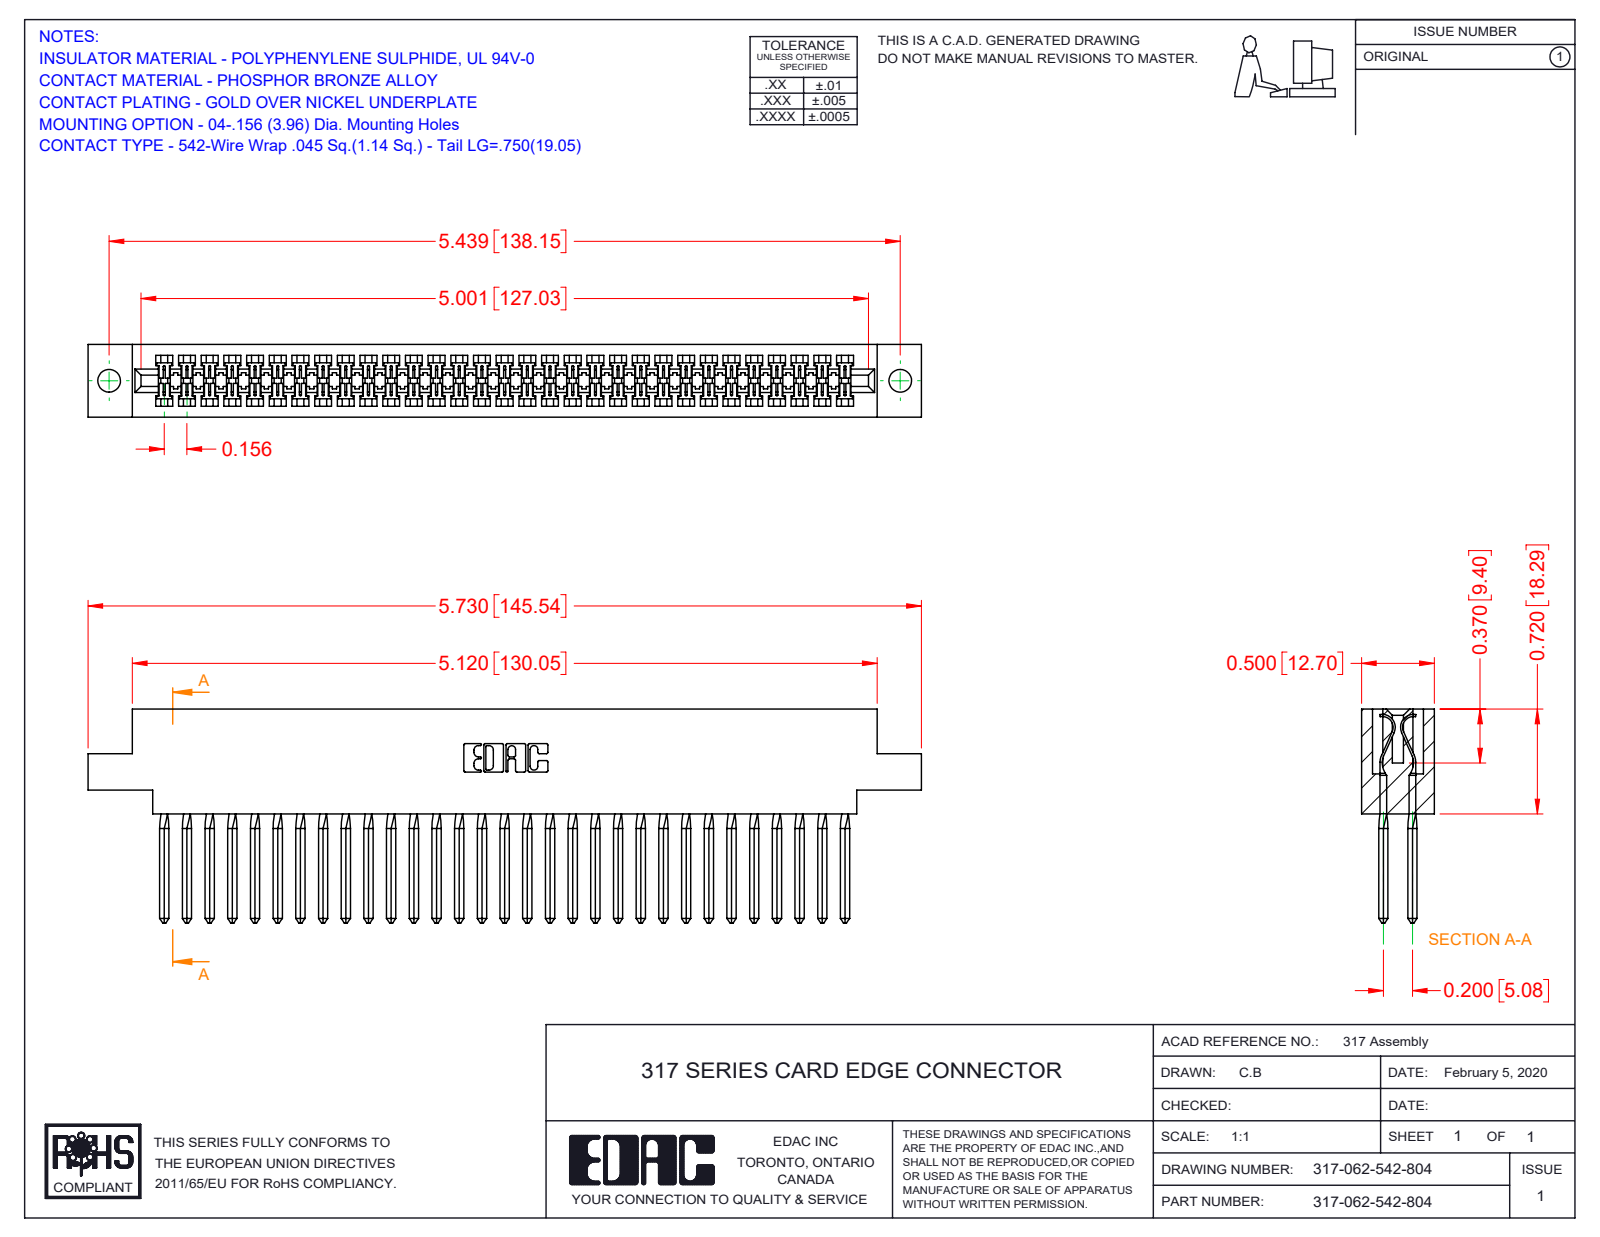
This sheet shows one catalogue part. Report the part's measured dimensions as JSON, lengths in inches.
{"part_name": "317-290-003_542; 317-062-542-804; 317 Part_.156 Dia - TH", "step_written_by": "SolidWorks 2016 (CONFIG_CONTROL_DESIGN)", "units": "inches", "bodies": {"solids": 63, "faces": 3636, "planar": 2910, "cylindrical": 478, "other": 248}, "overall_size": [5.73, 1.47, 0.5], "volume_in3": 1.428, "surface_area_in2": 49.6, "round_holes": [[0.156, 2]], "partial_cylinders_radius": [[0.006, 124], [0.01, 22], [0.007, 6], [0.031, 6], [0.026, 3], [0.074, 2], [0.089, 2], [0.1, 2]], "face_to_face_distances": [0.5, 0.075, 0.425, 0.35, 0.2, 0.11, 0.116, 0.046, 0.128, 0.372], "hole_center_spacings": [5.439]}
